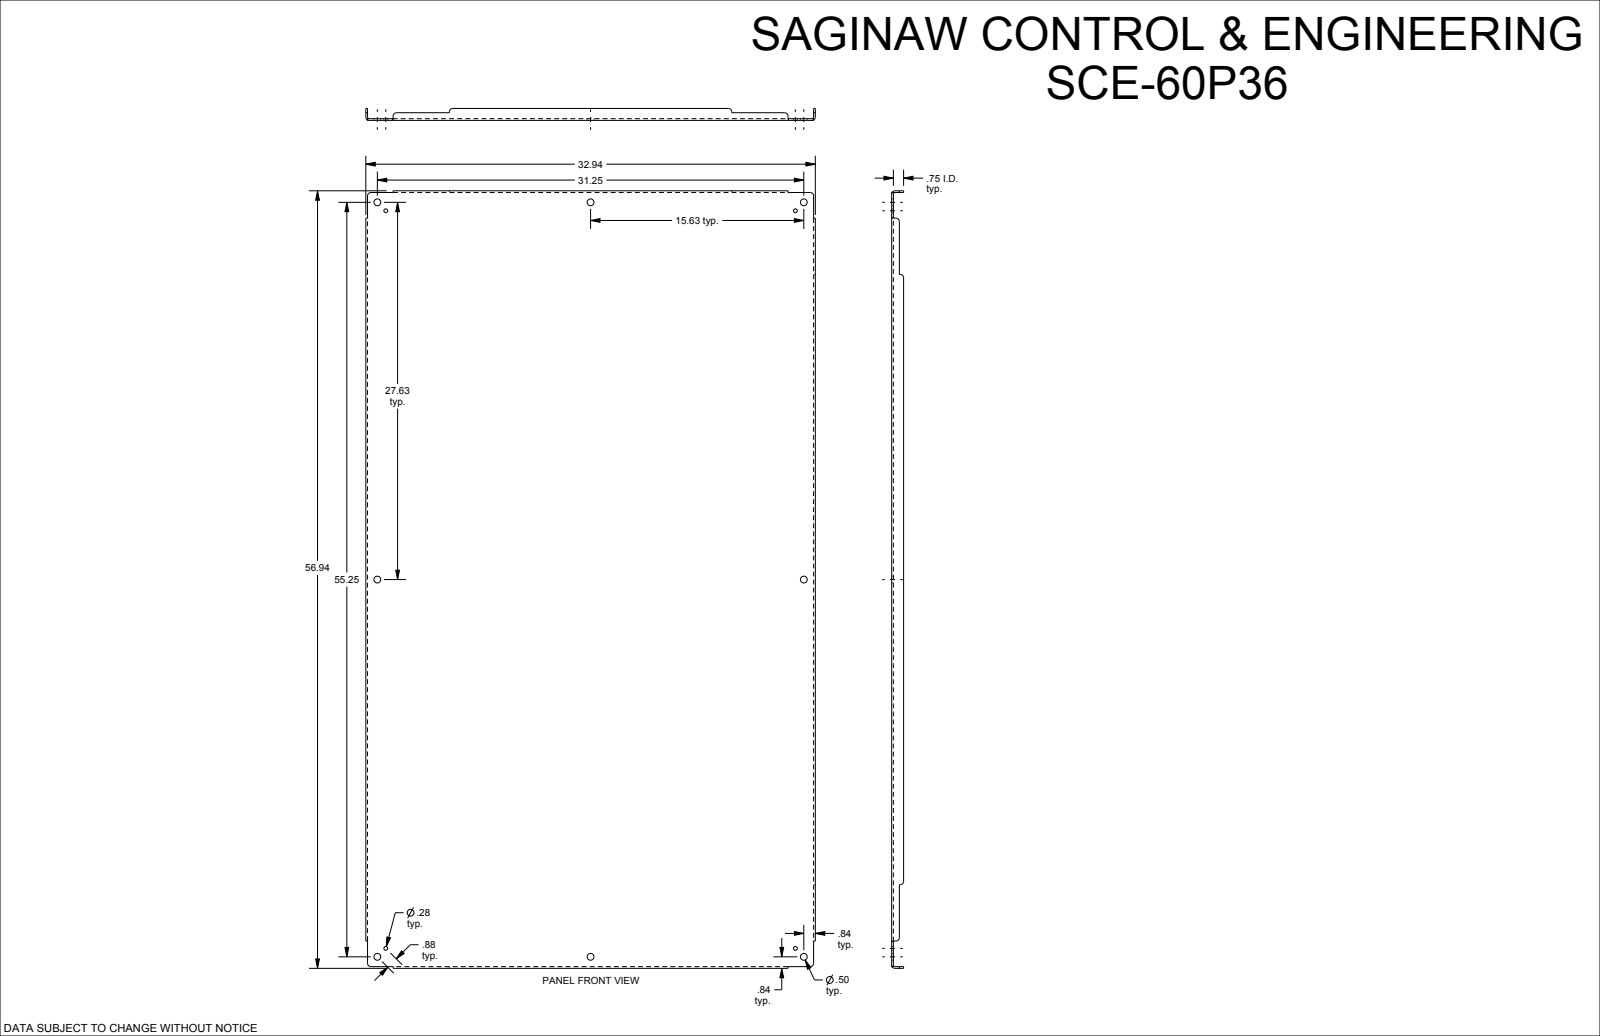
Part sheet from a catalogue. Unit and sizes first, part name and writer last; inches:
Units: inches
Overall size (bounding box): 56.938 × 32.938 × 0.875
Round holes (diameter × count): ⌀0.5 ×8, ⌀0.281 ×4
Partial cylindrical surfaces — rounded edges, fillets, slot ends (radius × count): R0.25 ×12, R0.112 ×4, R0.237 ×4
Main face-to-face distances: 0.125, 0.125, 32.813, 56.813, 32.687, 32.938, 56.687, 0.75, 0.875, 56.938
Hole centre spacings: 0.875, 15.019, 15.625, 27.013, 27.625, 30.638, 31.738, 40.837
Volume: 246.4 in³ · Surface area: 3 968 in²
Bodies: 1 solid, 110 faces (46 planar, 40 cylindrical, 24 other)
Part name (STEP PRODUCT): SCE-60P36
STEP written by: SolidWorks 2019 (CONFIG_CONTROL_DESIGN)
